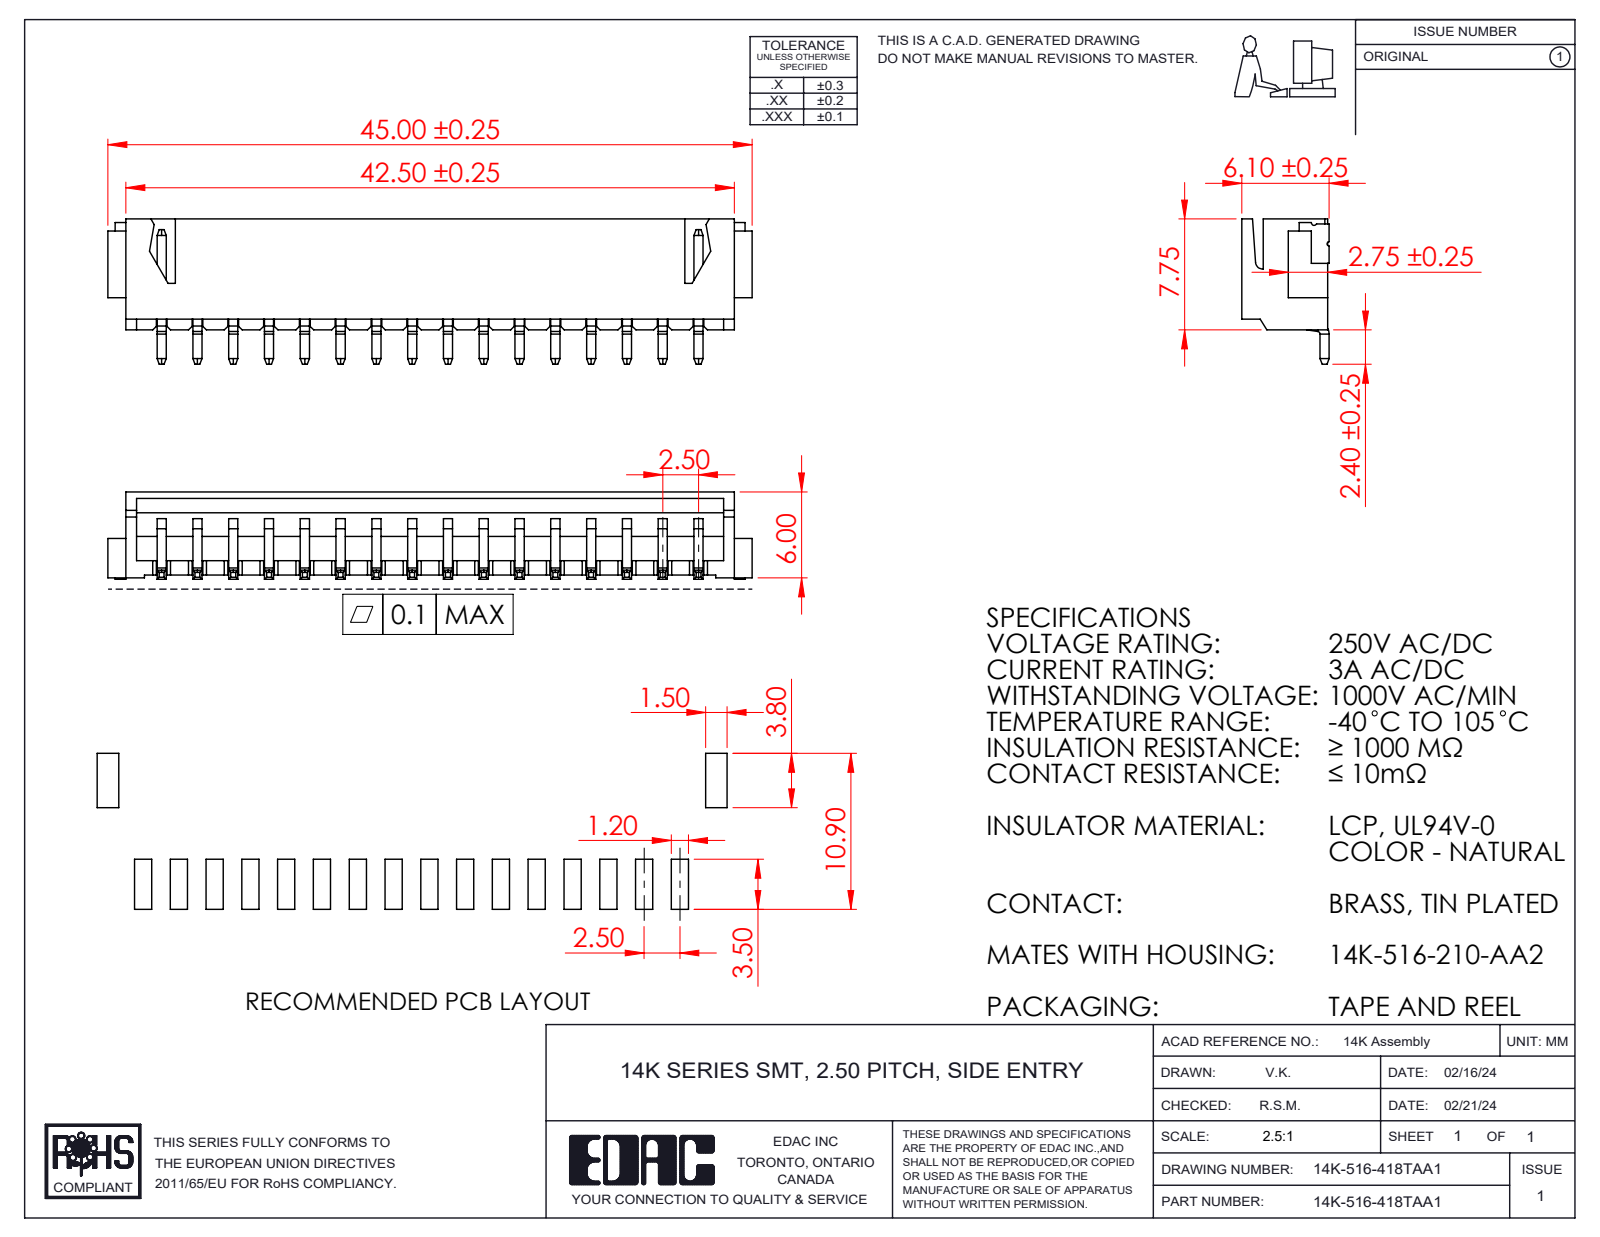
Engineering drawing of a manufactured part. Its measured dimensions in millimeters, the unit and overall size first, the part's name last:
Units: millimetres
Overall size (bounding box): 45 × 10.15 × 6.1
Partial cylindrical surfaces — rounded edges, fillets, slot ends (radius × count): R0.38 ×32, R0.18 ×2, R0.82 ×2, R0.14 ×1, R0.2 ×1, R0.5 ×1
Main face-to-face distances: 0.75, 5.05, 5.8, 4.3, 2.5, 1.24, 0.5, 0.64, 1, 1.75
Volume: 775 mm³ · Surface area: 2 515 mm²
Bodies: 17 solids, 917 faces (814 planar, 103 cylindrical, 0 other)
Part name (STEP PRODUCT): 14K Series SMT Pin_Side Entry; 14K-516-418TAA1; 14K Series SMT Side Entry Insulator_516
STEP written by: SolidWorks 2023 (CONFIG_CONTROL_DESIGN)
